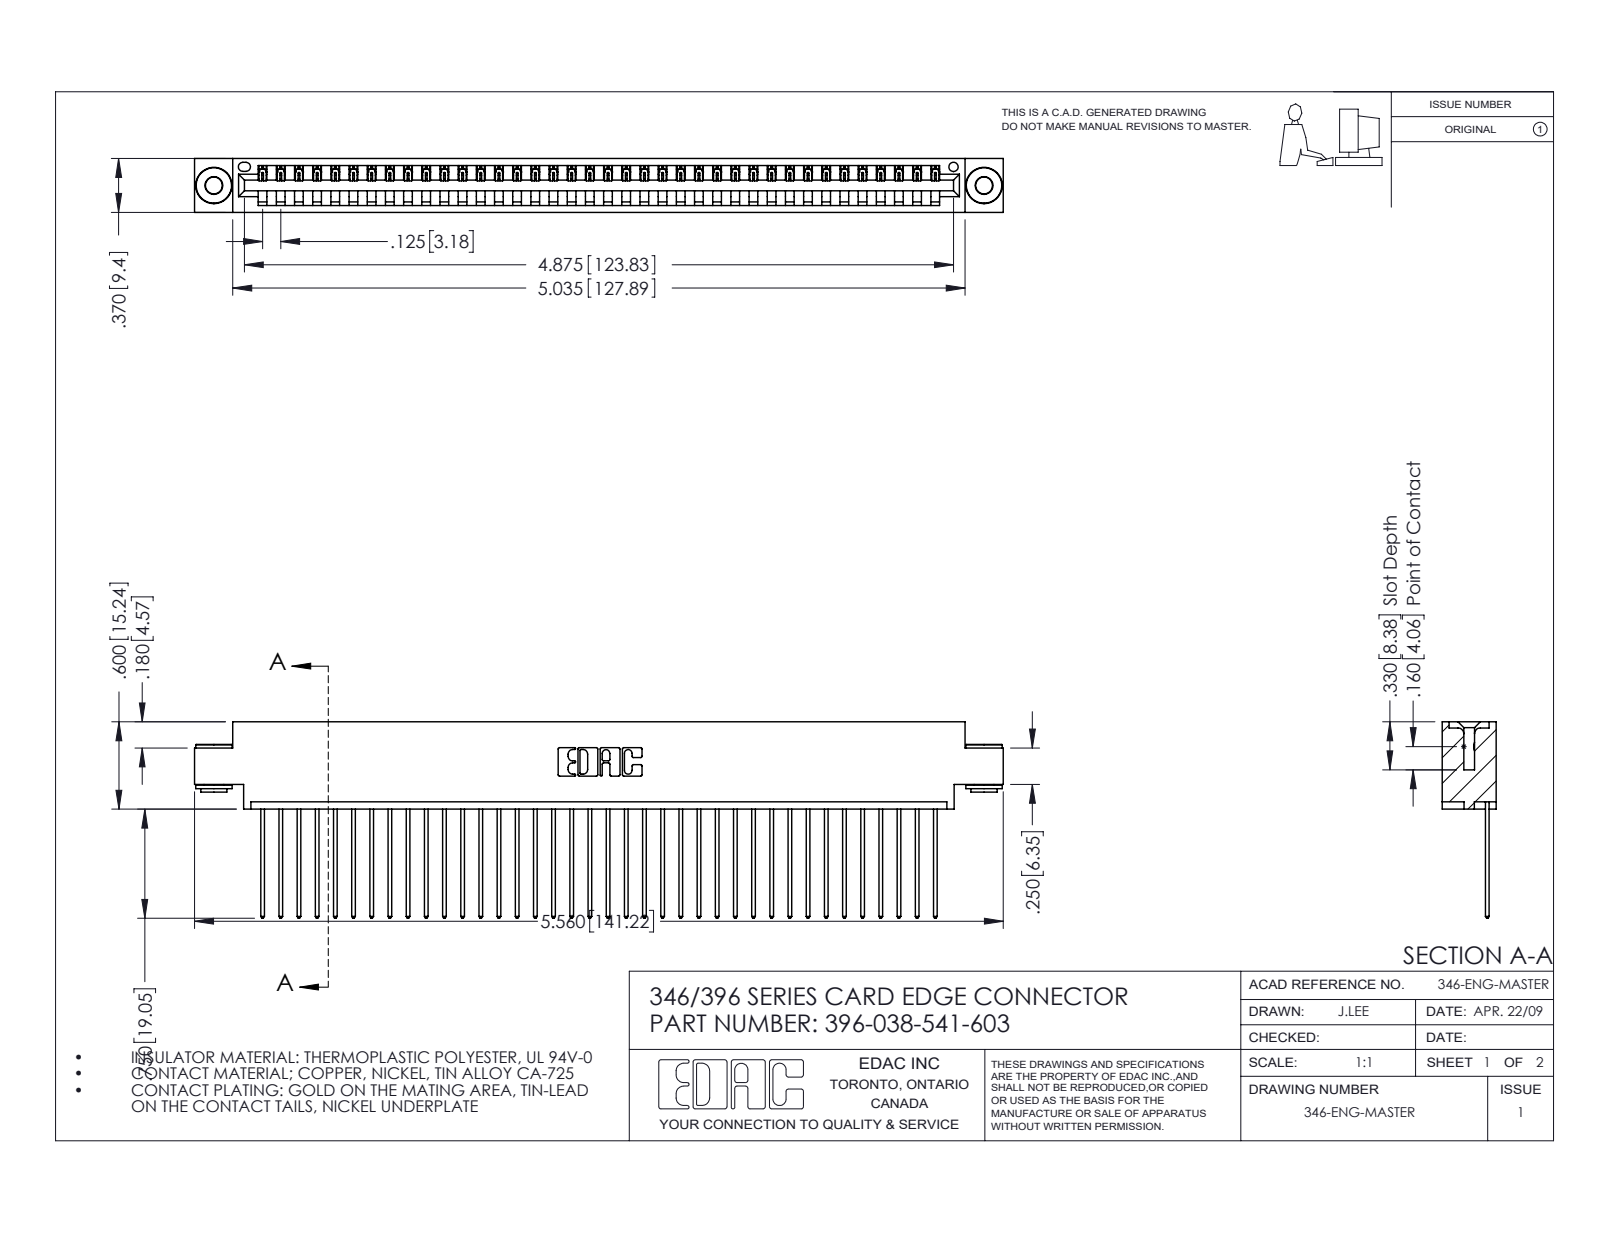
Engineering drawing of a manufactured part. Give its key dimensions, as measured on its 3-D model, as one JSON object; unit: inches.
{"part_name": "396-038-541-603; 345-292-001_345-293-141; 346 Part_0.170 Offset - 0.156 Dia-TH; 345-250-002_345-250-002-102", "step_written_by": "SolidWorks 2016 (CONFIG_CONTROL_DESIGN)", "units": "inches", "bodies": {"solids": 41, "faces": 2368, "planar": 1610, "cylindrical": 750, "other": 8}, "overall_size": [5.56, 1.35, 0.37], "volume_in3": 0.823, "surface_area_in2": 27.8, "round_holes": [[0.116, 2], [0.156, 2], [0.064, 1]], "round_bosses_or_shafts": [[0.25, 2], [0.18, 2], [0.136, 2]], "partial_cylinders_radius": [[0.006, 76], [0.01, 76], [0.01, 22], [0.007, 6], [0.031, 6], [0.026, 3], [0.031, 2], [0.04, 2]], "face_to_face_distances": [0.048, 0.322, 0.37, 0.25, 0.025, 0.072, 0.298, 0.148, 0.222, 0.1], "hole_center_spacings": [0.246, 5.086, 5.295]}
